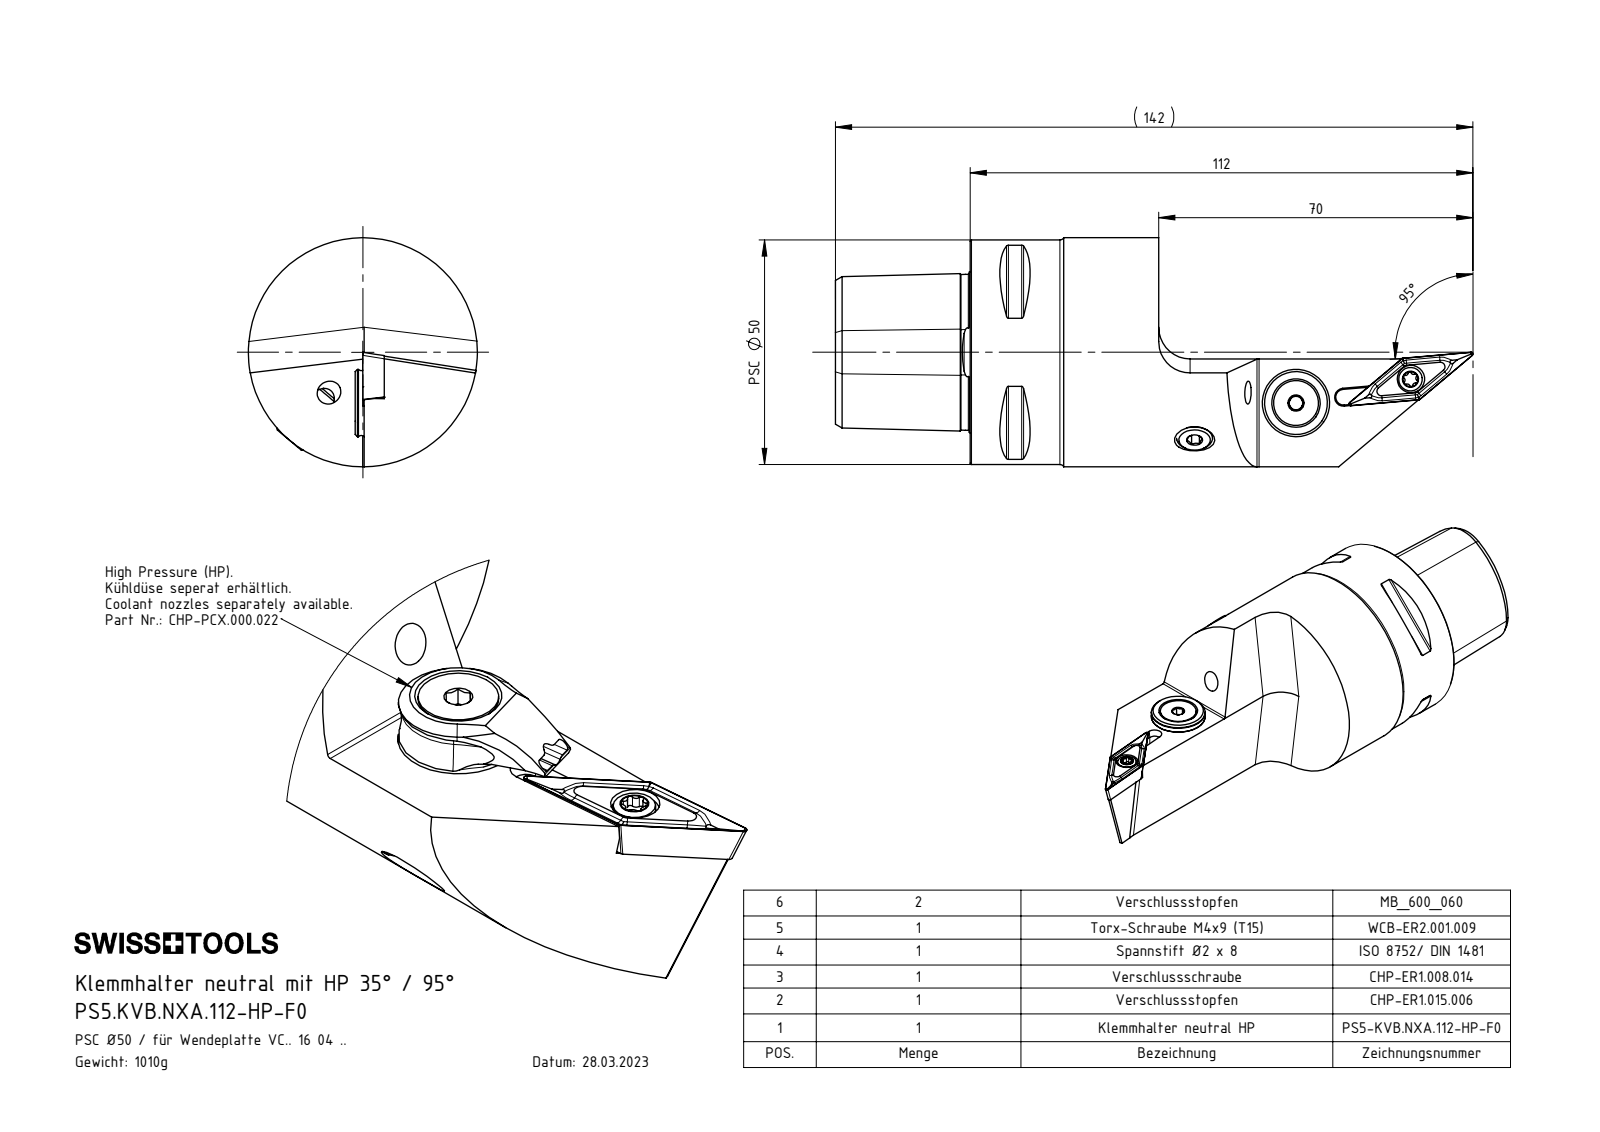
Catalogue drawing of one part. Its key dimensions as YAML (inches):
part_name: "CHP-ER1.008.014_A; CHP-ER1.015.006; DIN 7991 - M5x15; DIN 3771 - 13x1 (+7 more)"
step_written_by: "SolidWorks 2017 (AUTOMOTIVE_DESIGN)"
units: inches
bodies: {solids: 12, faces: 460, planar: 95, cylindrical: 123, other: 242}
overall_size: [5.591, 2.008, 2.008]
volume: 7.843
surface_area: 42.67
round_holes:
  - {diameter: 0.197, count: 7}
  - {diameter: 0.165, count: 2}
  - {diameter: 0.236, count: 2}
  - {diameter: 0.24, count: 2}
  - {diameter: 0.047, count: 1}
  - {diameter: 0.079, count: 1}
  - {diameter: 0.098, count: 1}
  - {diameter: 0.118, count: 1}
  - {diameter: 0.13, count: 1}
  - {diameter: 0.157, count: 1}
  - {diameter: 0.173, count: 1}
  - {diameter: 0.205, count: 1}
round_bosses_or_shafts:
  - {diameter: 0.236, count: 2}
  - {diameter: 2.008, count: 1}
  - {diameter: 1.969, count: 1}
  - {diameter: 0.591, count: 1}
  - {diameter: 0.528, count: 1}
  - {diameter: 0.394, count: 1}
  - {diameter: 0.315, count: 1}
  - {diameter: 0.217, count: 1}
partial_cylinders:
  - {radius: 0.02, count: 9}
  - {radius: 0.013, count: 6}
  - {radius: 0.023, count: 6}
  - {radius: 0.276, count: 3}
  - {radius: 0.069, count: 1}
  - {radius: 0.157, count: 1}
face_to_face_distances: [1.654, 1.181, 2.835, 0.177, 0.176, 0.755, 1.748, 0.394, 0.787, 2.047]
hole_center_spacings: [0.177, 0.905, 0.909, 1.024, 1.025, 1.03, 2.426, 2.505]
